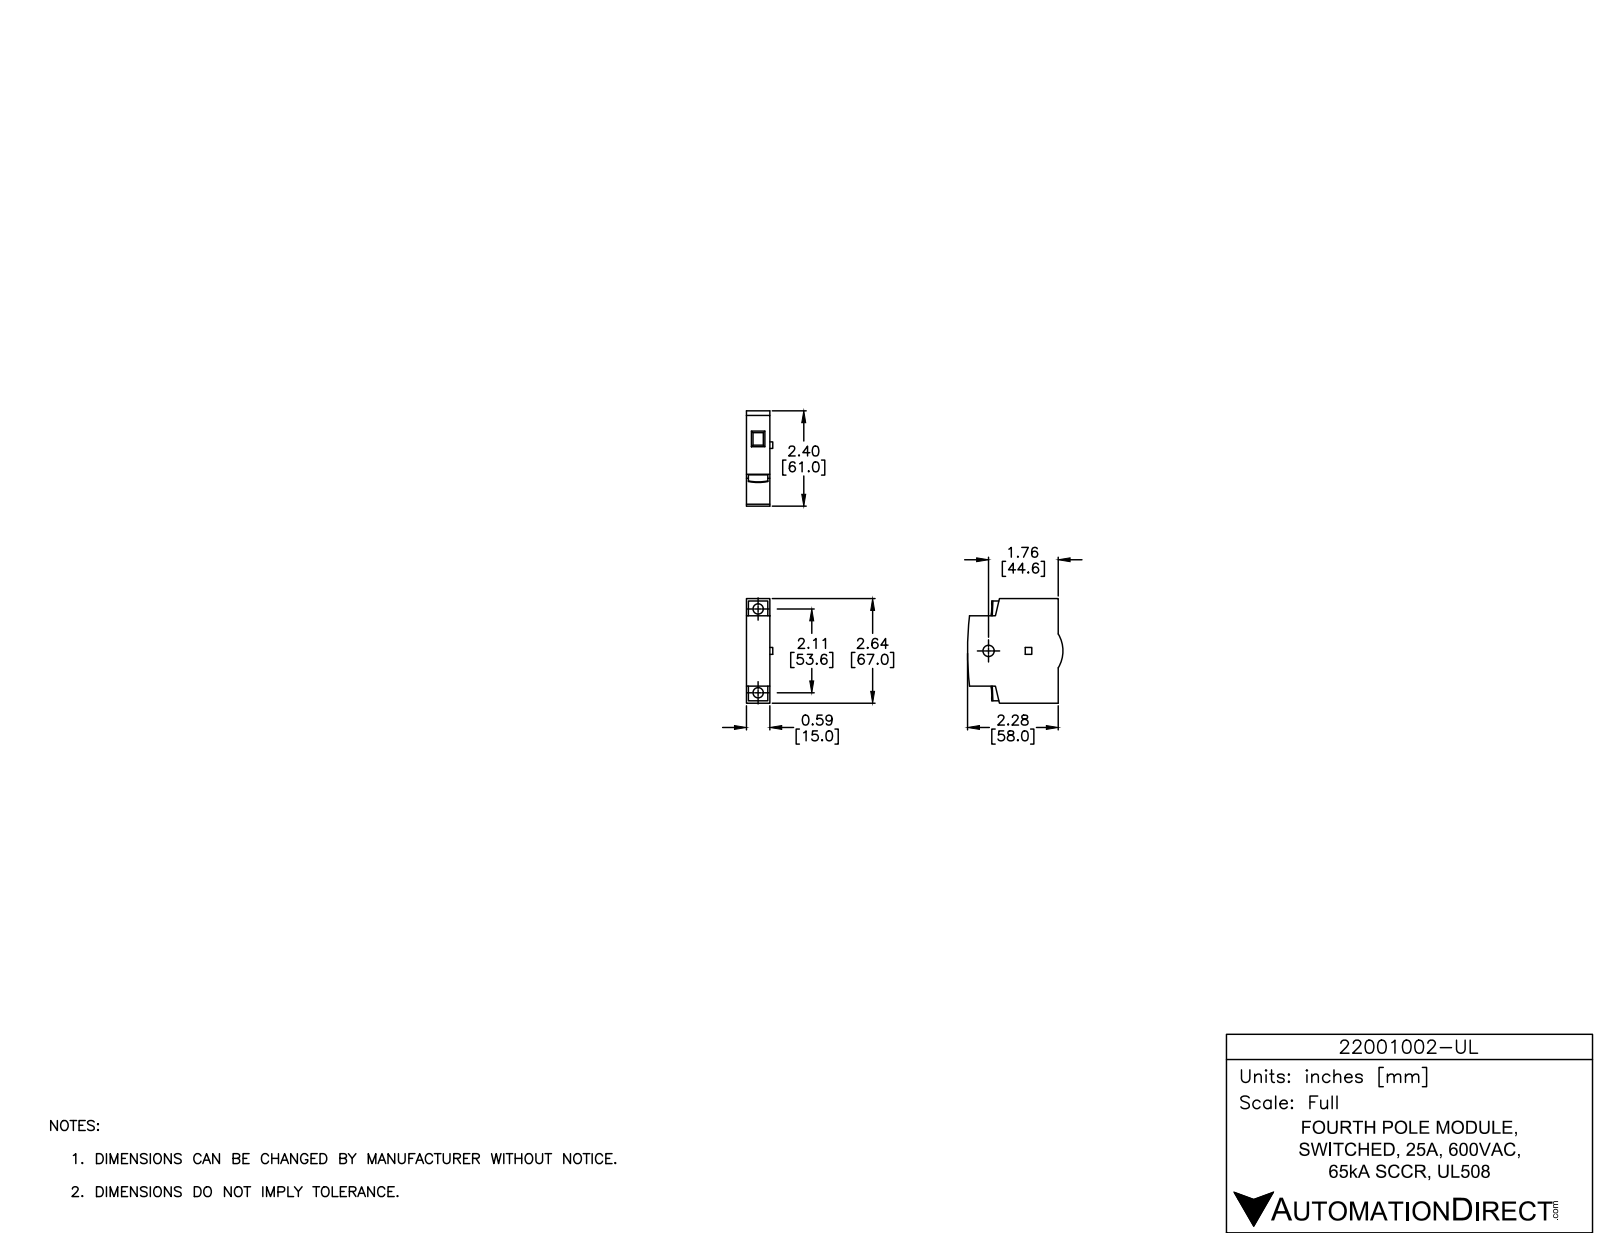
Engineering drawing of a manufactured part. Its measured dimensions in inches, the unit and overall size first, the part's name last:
Units: inches
Overall size (bounding box): 2.638 × 2.402 × 0.665
Round holes (diameter × count): ⌀0.26 ×2, ⌀0.283 ×1
Partial cylindrical surfaces — rounded edges, fillets, slot ends (radius × count): R0.827 ×1, R7.874 ×1
Main face-to-face distances: 0.591, 2.638, 0.433, 2.205, 1.772, 0.063, 2.575, 0.37, 2.142, 0.051
Hole centre spacings: 2.11
Volume: 3.141 in³ · Surface area: 18.13 in²
Bodies: 1 solid, 61 faces (46 planar, 11 cylindrical, 4 other)
Part name (STEP PRODUCT): 22001002-UL
STEP written by: SolidWorks 2015 (AUTOMOTIVE_DESIGN)
